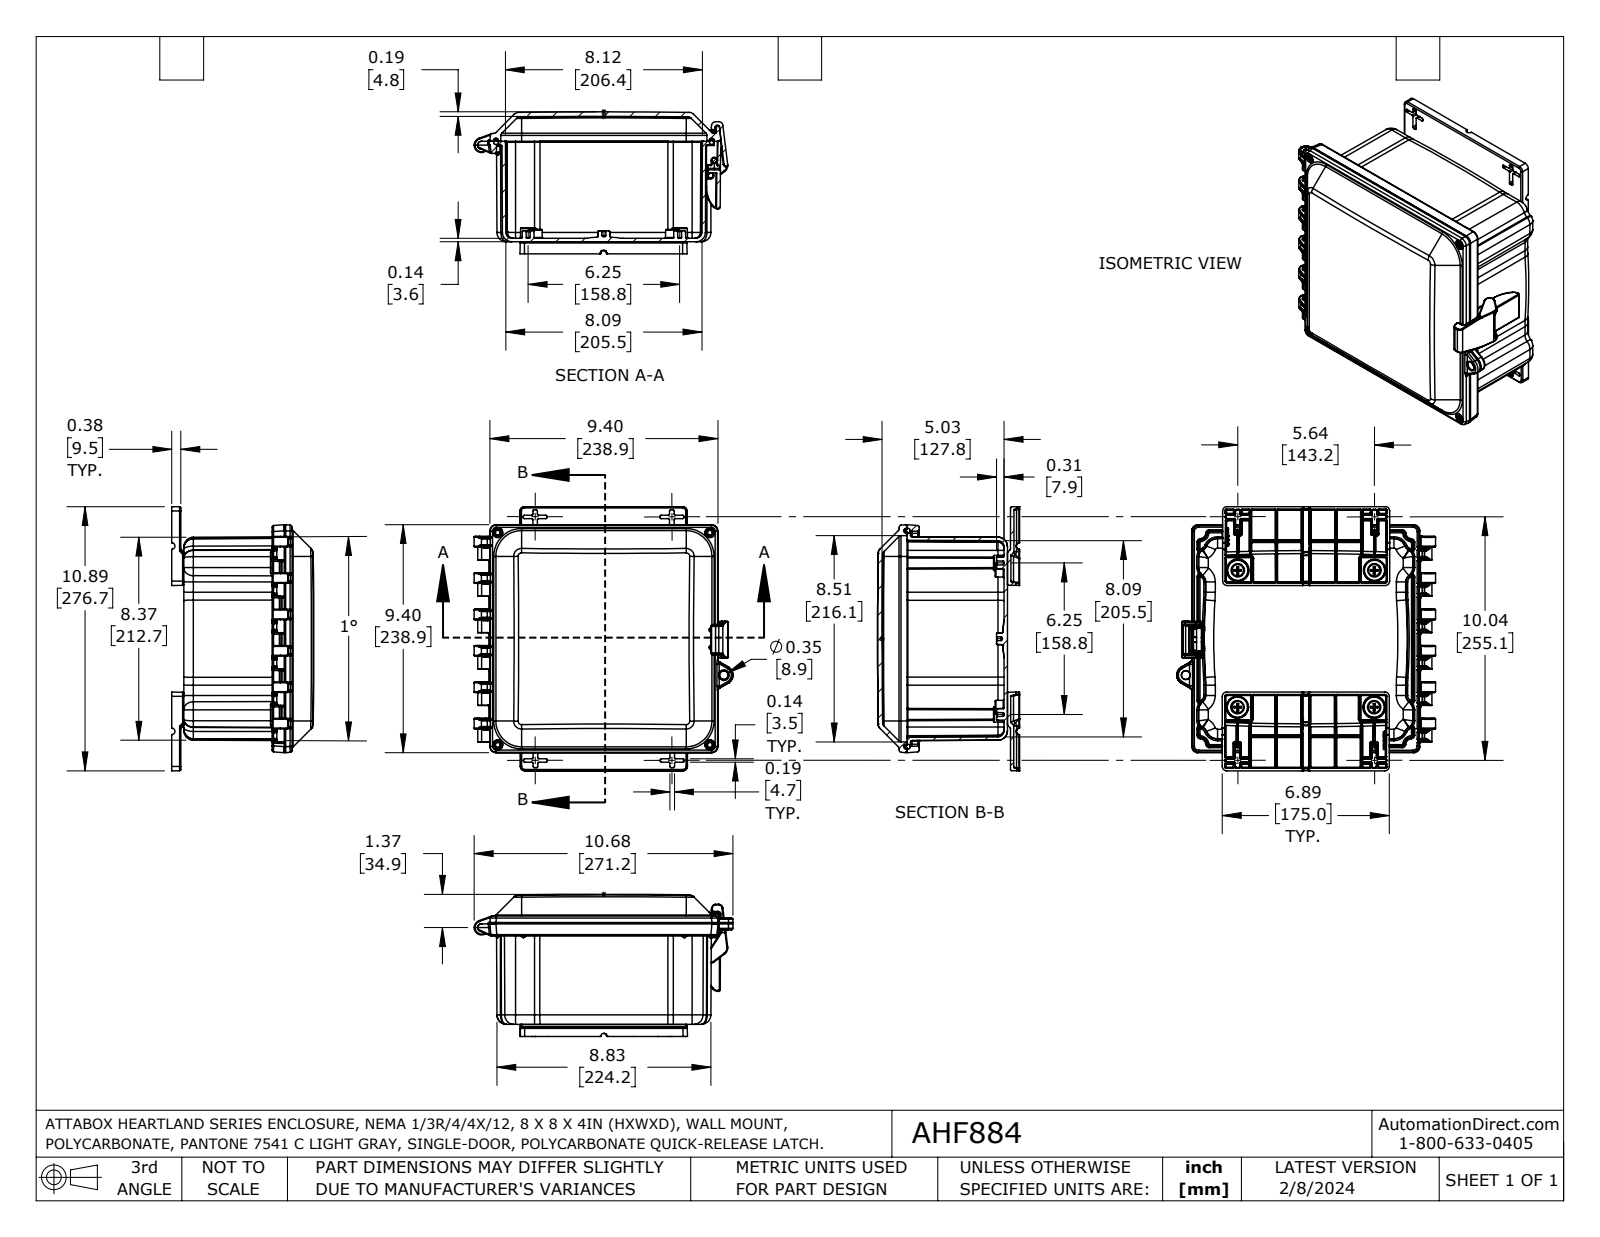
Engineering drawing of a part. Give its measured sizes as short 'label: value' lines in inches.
name: AHF884C
written by: SolidWorks 2023 (AUTOMOTIVE_DESIGN)
unit: in
bodies: 4 solids, 1157 faces (406 planar, 341 cylindrical, 410 other)
size: 10.892 × 10.676 × 5.858
volume: 80.25 in³; area: 810.5 in²
holes: 5× ⌀0.187, 4× ⌀0.195, 4× ⌀0.25, 4× ⌀0.26, 4× ⌀0.39, 2× ⌀0.27, 1× ⌀0.327, 1× ⌀0.375, 1× ⌀0.45
bosses: 5× ⌀0.487, 4× ⌀0.625, 4× ⌀0.25, 2× ⌀0.2, 1× ⌀0.313
rounds: 110× R0.035, 21× R0.02, 12× R0.01, 11× R0.065, 8× R0.05, 8× R0.329, 6× R0.095, 4× R0.06
face distances: 0.124, 8.124, 4.14, 0.5, 0.14, 8, 8.247, 4, 0.64, 4.64
hole spacings: 7.604, 3.125, 4.55, 8.75, 6.988, 8.683, 8.683, 10.607
